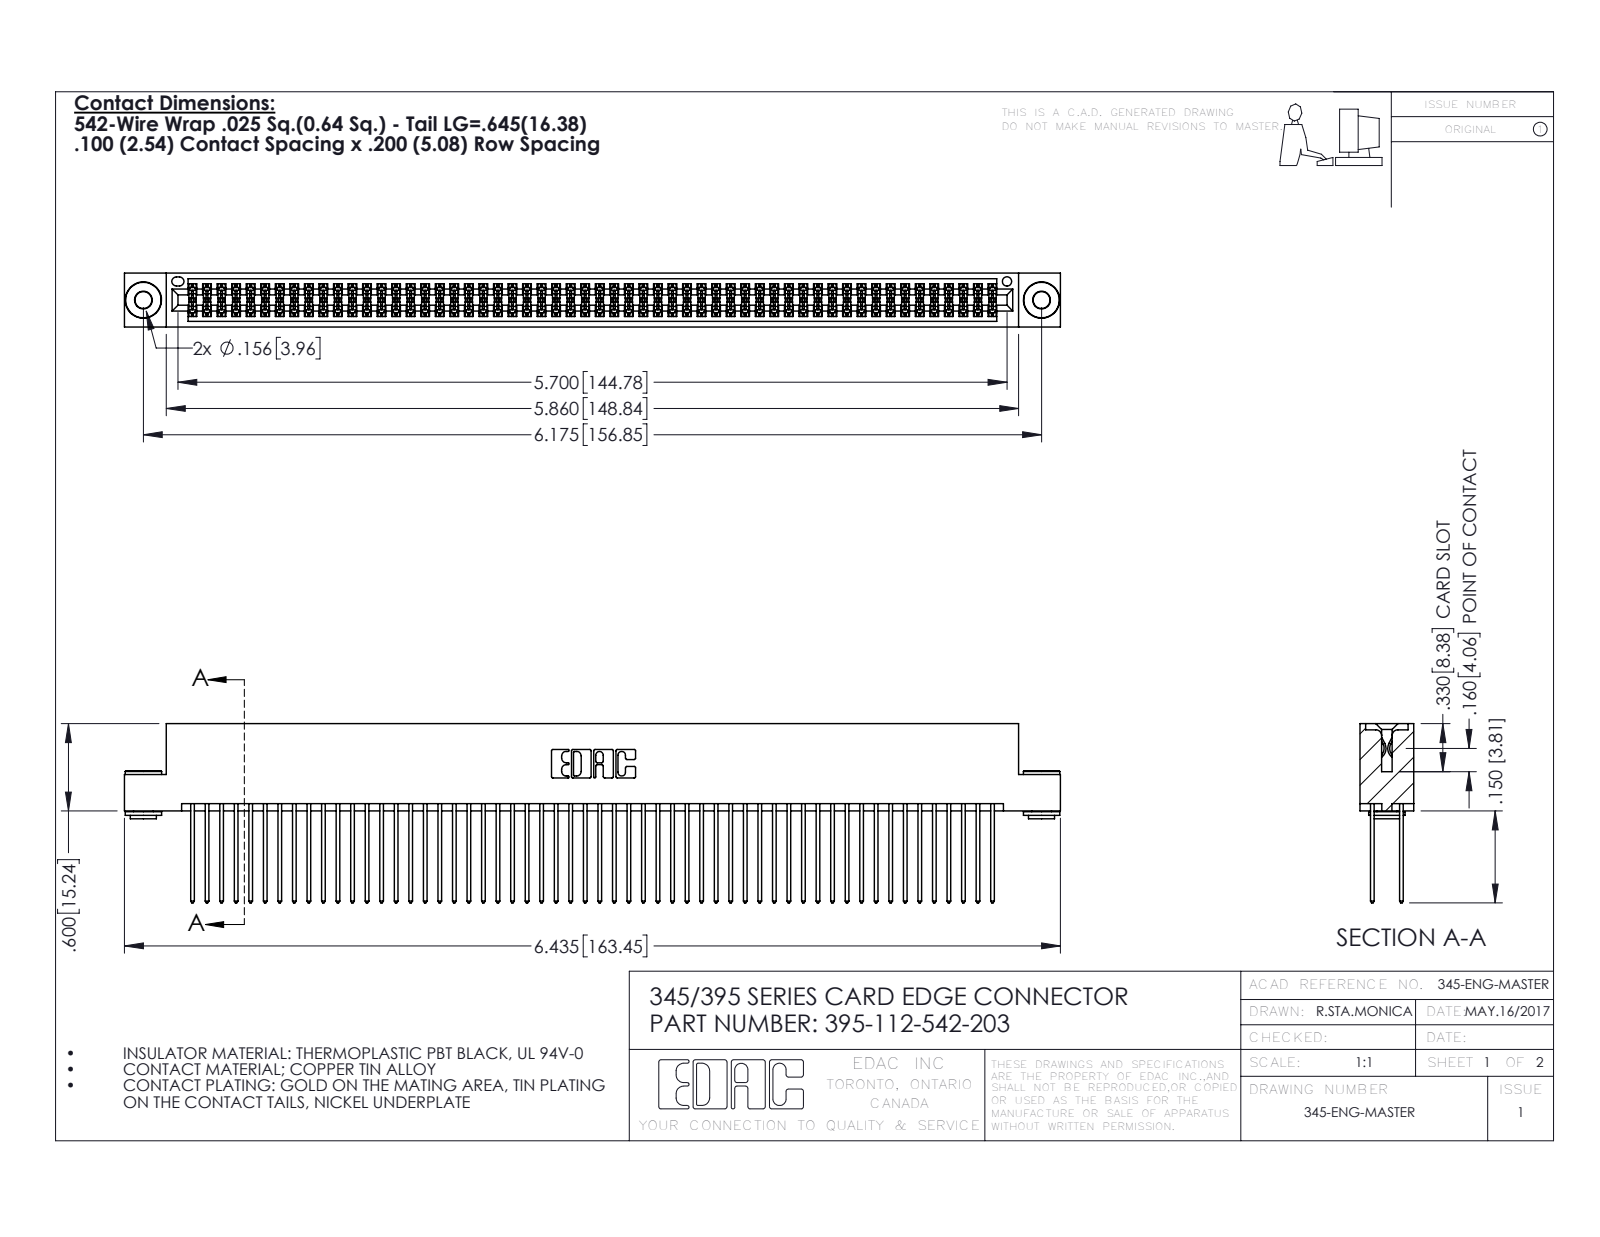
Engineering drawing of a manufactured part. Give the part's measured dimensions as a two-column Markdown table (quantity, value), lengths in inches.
| quantity | value |
| --- | --- |
| part name | 345-292-001_345-293-142; 345 Part_Flush Mounting Lugs - 0.156 Dia-TH; 345-250-002_345-250-002-102; 395-112-542-203 |
| STEP written by | SolidWorks 2016 (CONFIG_CONTROL_DESIGN) |
| units | inches |
| bodies | 115 solids, 5764 faces (3786 planar, 1970 cylindrical, 8 other) |
| overall size | 6.435 × 1.232 × 0.37 |
| volume | 1.01 in³ |
| surface area | 42.44 in² |
| round holes (diameter × count) | 0.116 × 2, 0.156 × 2, 0.064 × 1 |
| round bosses / shafts (diameter × count) | 0.25 × 2, 0.18 × 2, 0.136 × 2 |
| partial cylindrical surfaces (radius × count) | 0.006 × 168, 0.01 × 112, 0.01 × 22, 0.007 × 6, 0.031 × 6, 0.026 × 3, 0.014 × 2, 0.019 × 2 |
| main face-to-face distances | 0.072, 0.298, 0.2, 0.025, 0.098, 0.272, 0.225, 0.37, 0.175, 0.149 |
| hole center spacings | 0.27, 5.939, 6.175 |
